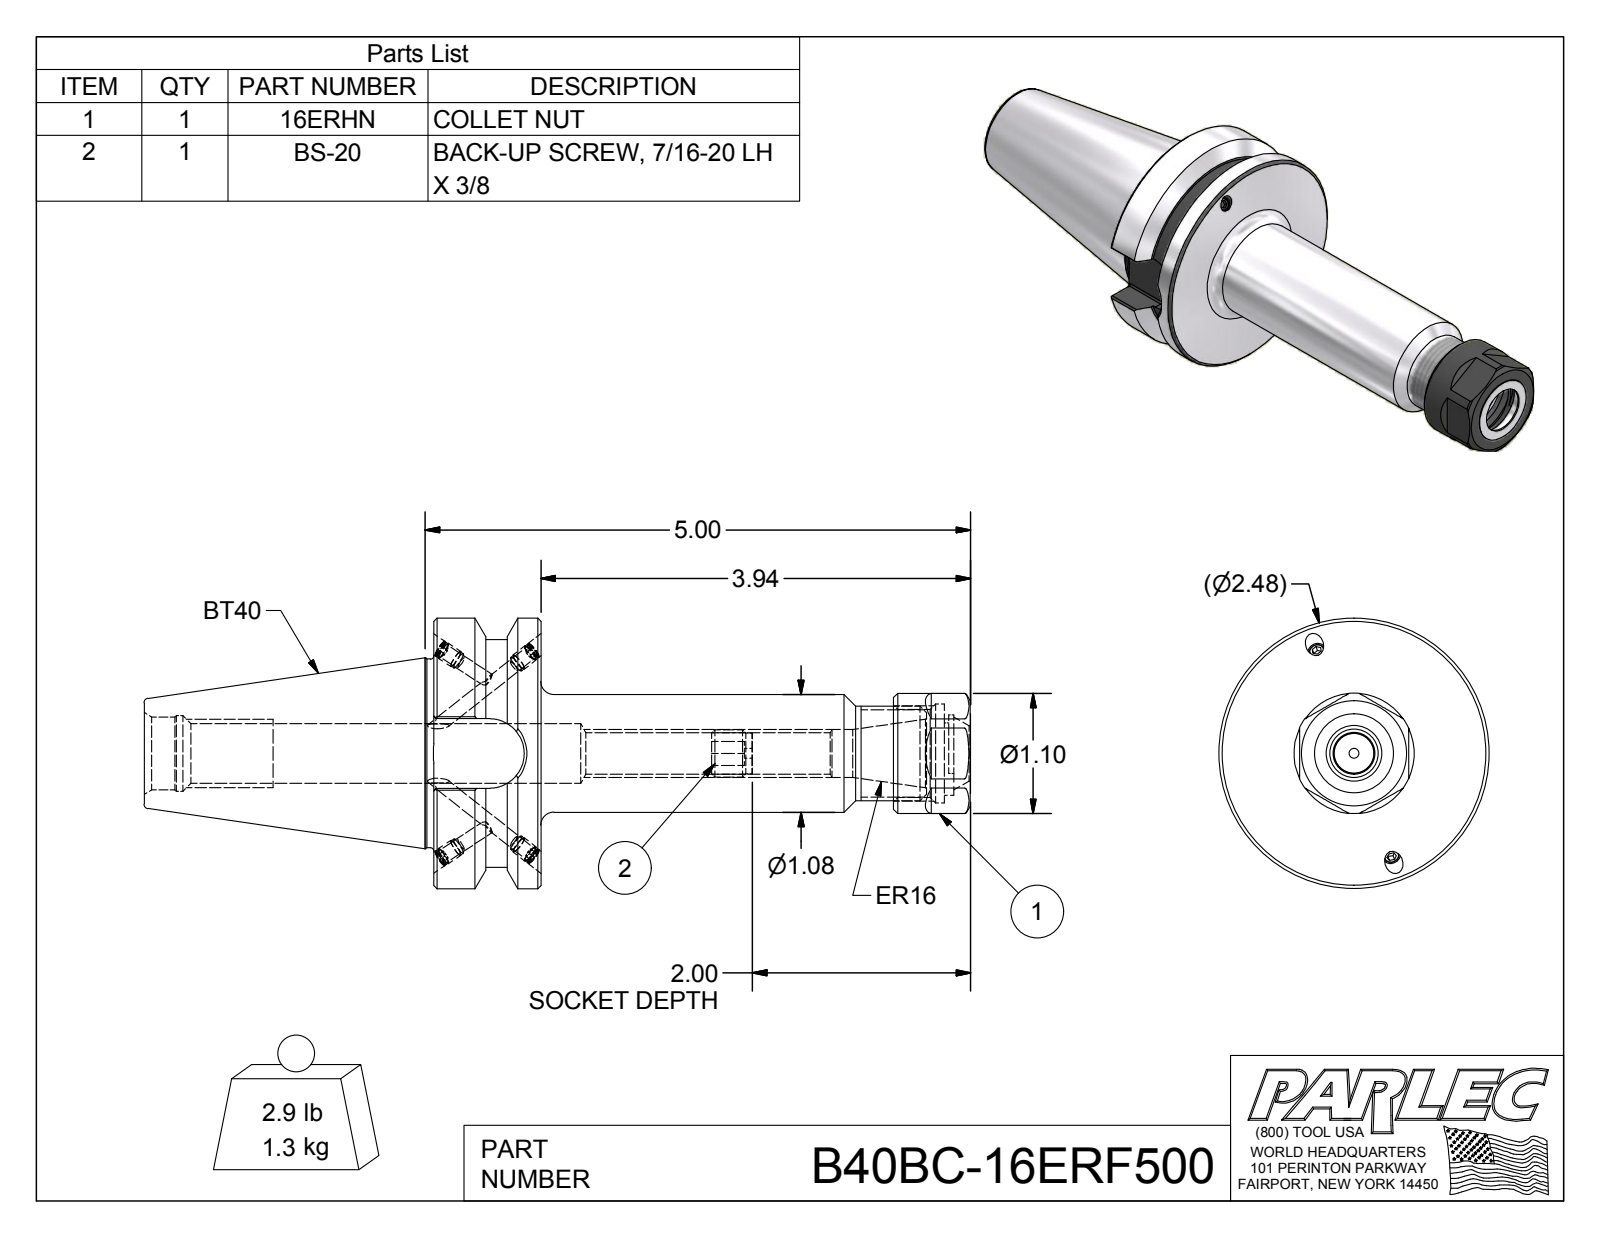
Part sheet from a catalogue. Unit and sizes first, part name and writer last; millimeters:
Units: millimetres
Overall size (bounding box): 192.41 × 62.99 × 62.99
Round holes (diameter × count): ⌀3.3 ×4, ⌀4.1 ×4, ⌀2.29 ×1, ⌀9.73 ×1, ⌀11.18 ×1, ⌀12.4 ×1, ⌀13.84 ×1, ⌀17.01 ×1, ⌀17.02 ×1, ⌀17.62 ×1, ⌀20.5 ×1, ⌀23 ×1
Round bosses / shafts (diameter × count): ⌀4.2 ×4, ⌀4 ×4, ⌀62.99 ×1, ⌀53.01 ×1, ⌀43.94 ×1, ⌀28 ×1, ⌀27.43 ×1, ⌀22 ×1
Partial cylindrical surfaces — rounded edges, fillets, slot ends (radius × count): R0.51 ×8, R7.24 ×1, R8.09 ×1, R9 ×1
Main face-to-face distances: 24.99, 125.02, 100.03, 25.14, 45.22, 10.04, 35.18, 119.32, 94.33, 5.7
Hole centre spacings: 1.52
Volume: 164 793 mm³ · Surface area: 38 043 mm²
Bodies: 7 solids, 201 faces (93 planar, 53 cylindrical, 55 other)
Part name (STEP PRODUCT): B40BCB-16ER5-1; 029-965; 16ERHN; BS-20 (+1 more)
STEP written by: Autodesk Inventor 2016 (AUTOMOTIVE_DESIGN)
